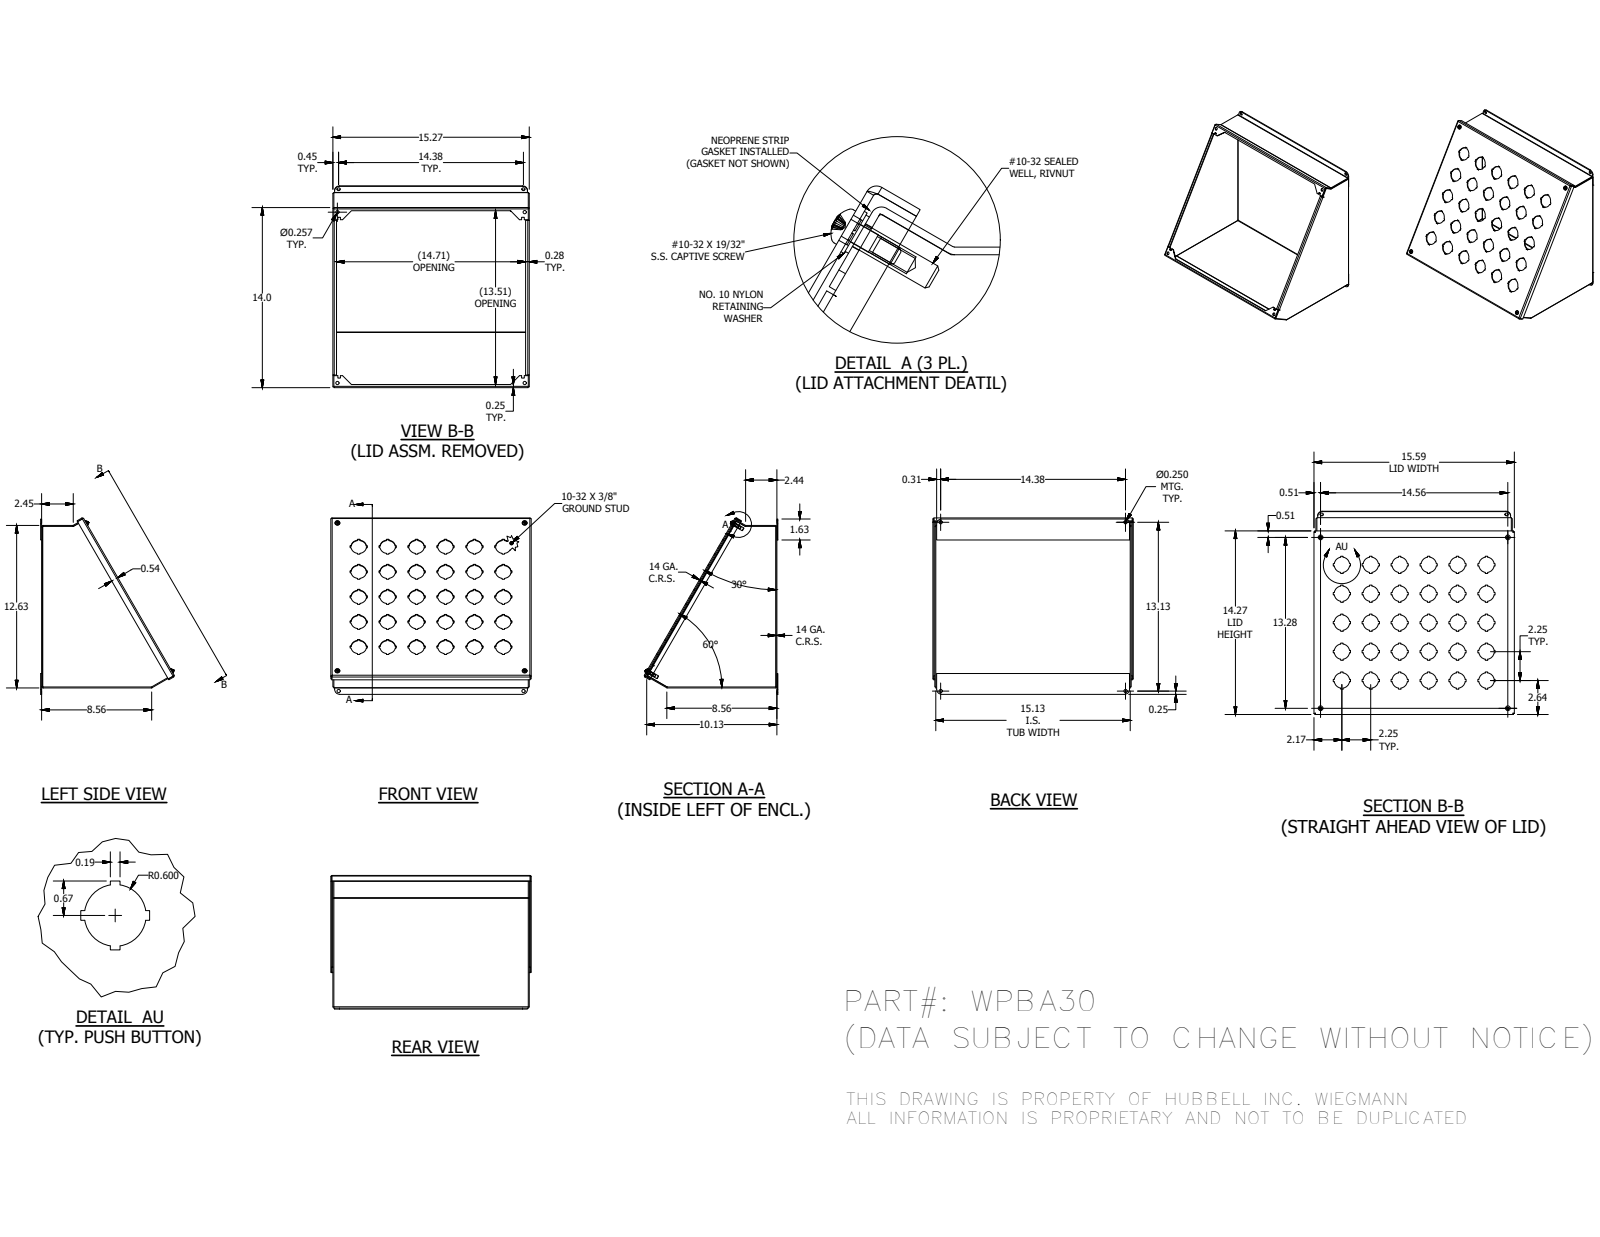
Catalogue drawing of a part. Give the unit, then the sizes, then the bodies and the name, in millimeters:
Units: millimetres
Overall size (bounding box): 395.91 × 348.57 × 263.92
Round holes (diameter × count): ⌀30.48 ×30, ⌀3.96 ×4, ⌀4.98 ×4, ⌀6.35 ×4, ⌀6.53 ×4, ⌀7.06 ×4, ⌀7.14 ×4
Round bosses / shafts (diameter × count): ⌀4.83 ×5, ⌀11.51 ×4, ⌀10.31 ×4, ⌀9.47 ×4, ⌀6.3 ×4, ⌀6.35 ×1
Partial cylindrical surfaces — rounded edges, fillets, slot ends (radius × count): R0.79 ×12, R2.67 ×12, R2.27 ×4, R9.53 ×4
Main face-to-face distances: 1.88, 1.87, 386.05, 386.06, 384.18, 387.93, 318.92, 3.76, 317.04, 320.8
Hole centre spacings: 127.79, 57.15, 80.82, 114.3, 171.45, 180.73, 206.05, 255.58
Volume: 1 022 000 mm³ · Surface area: 1 110 000 mm²
Bodies: 19 solids, 960 faces (651 planar, 210 cylindrical, 99 other)
Part name (STEP PRODUCT): WPBA30BKP; WPBA5ROWEWPR; WPBA5ROWEWPL; 34984 (+6 more)
STEP written by: Autodesk Inventor 2014 (AUTOMOTIVE_DESIGN)
